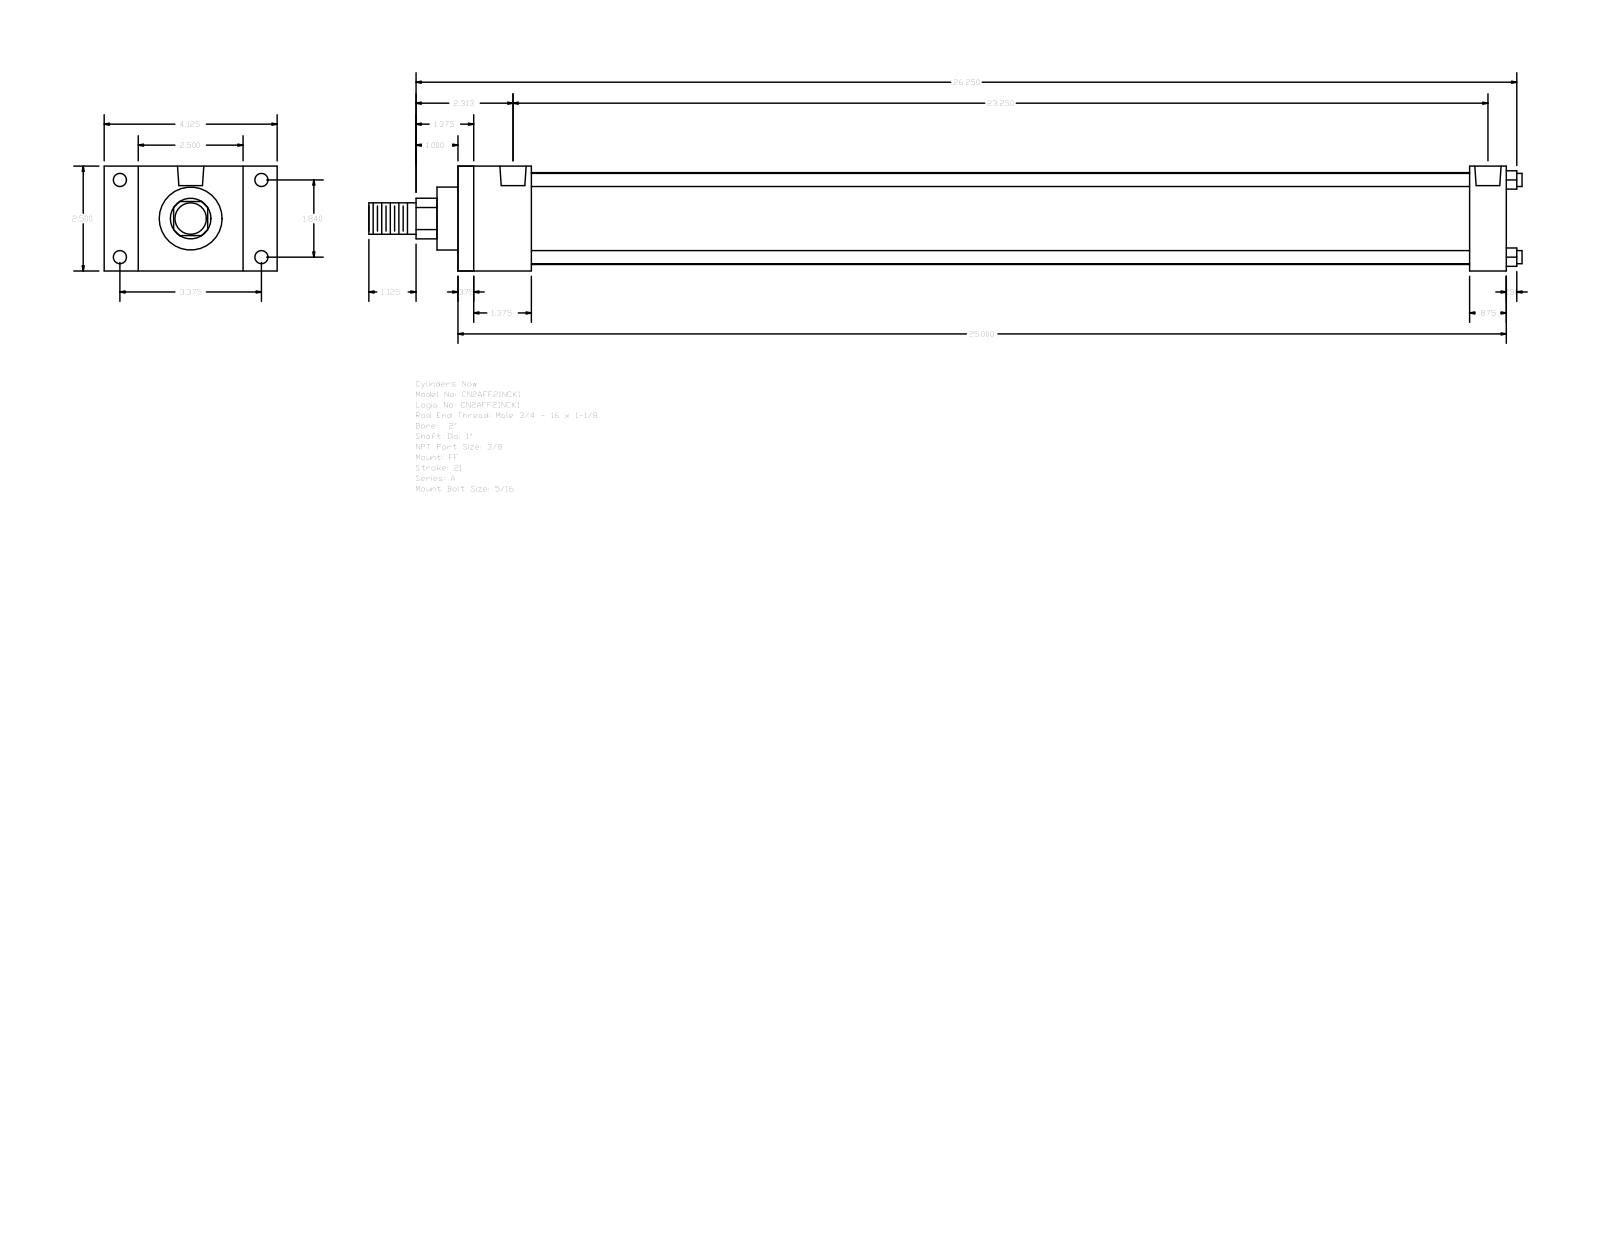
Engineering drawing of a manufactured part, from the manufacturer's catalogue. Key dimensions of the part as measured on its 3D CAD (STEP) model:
Part name (STEP PRODUCT): A_FF__0200_1
STEP written by: GSSL Pune (CONFIG_CONTROL_DESIGN)
Units: millimetres
Bodies: 0 solids, 92 faces (64 planar, 28 cylindrical, 0 other)
Overall size (bounding box): 698.5 × 104.78 × 63.5
Round holes (diameter × count): ⌀5.56 ×4, ⌀7.94 ×4, ⌀15.93 ×2
Round bosses / shafts (diameter × count): ⌀7.94 ×4, ⌀55.63 ×1, ⌀38.1 ×1, ⌀25.4 ×1, ⌀19.05 ×1
Partial cylindrical surfaces — rounded edges, fillets, slot ends (radius × count): R12.29 ×1
Main face-to-face distances: 63.5, 635, 9.52, 625.48, 20.64, 44.45, 612.77, 34.93, 603.25, 568.32
Hole centre spacings: 46.74, 85.72, 97.63, 584.98, 1.59, 3.98, 586.57, 588.96
